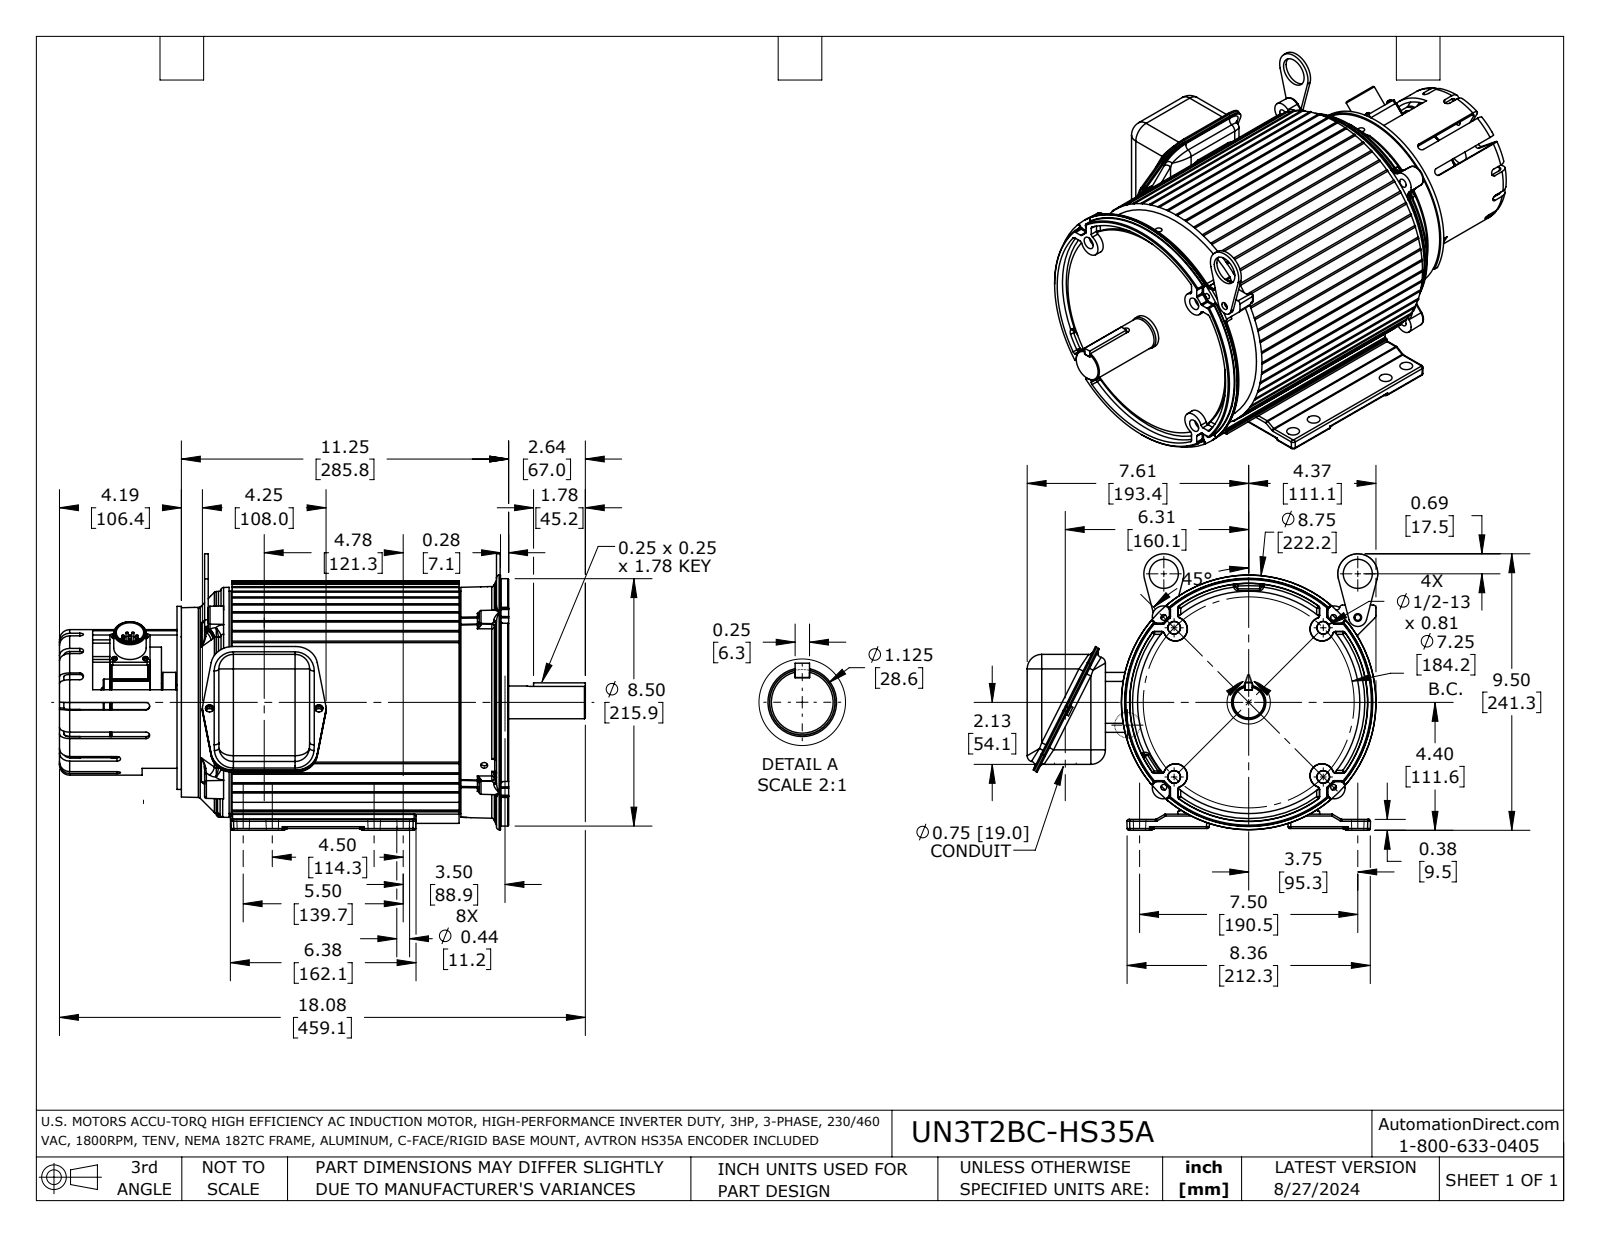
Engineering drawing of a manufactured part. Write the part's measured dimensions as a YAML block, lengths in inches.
part_name: "UN3T2BC-HS35A"
step_written_by: "SolidWorks 2021 (AUTOMOTIVE_DESIGN)"
units: inches
bodies: {solids: 22, faces: 2943, planar: 716, cylindrical: 783, other: 1444}
overall_size: [18.076, 12.052, 9.5]
volume: 617.1
surface_area: 1110
round_holes:
  - {diameter: 0.4, count: 6}
  - {diameter: 0.12, count: 4}
  - {diameter: 0.2, count: 4}
  - {diameter: 0.234, count: 4}
  - {diameter: 0.277, count: 4}
  - {diameter: 0.136, count: 3}
  - {diameter: 1, count: 3}
  - {diameter: 0.232, count: 2}
  - {diameter: 0.266, count: 2}
  - {diameter: 0.281, count: 2}
  - {diameter: 0.174, count: 1}
  - {diameter: 0.5, count: 1}
round_bosses_or_shafts:
  - {diameter: 0.072, count: 8}
  - {diameter: 0.175, count: 4}
  - {diameter: 0.12, count: 4}
  - {diameter: 0.15, count: 3}
  - {diameter: 0.328, count: 2}
  - {diameter: 0.072, count: 2}
  - {diameter: 8.5, count: 1}
  - {diameter: 8.315, count: 1}
partial_cylinders:
  - {radius: 0.063, count: 140}
  - {radius: 0.061, count: 52}
  - {radius: 0.031, count: 48}
  - {radius: 0.125, count: 37}
  - {radius: 0.06, count: 22}
  - {radius: 0.094, count: 20}
  - {radius: 0.5, count: 14}
  - {radius: 0.16, count: 10}
face_to_face_distances: [12.081, 2.033, 10.048, 1.08, 0.953, 11.002, 1.375, 2.455, 3.408, 13.456]
hole_center_spacings: [2.073, 3.387, 4.319, 1.5, 2.22, 0.754, 1.75, 2.475]
